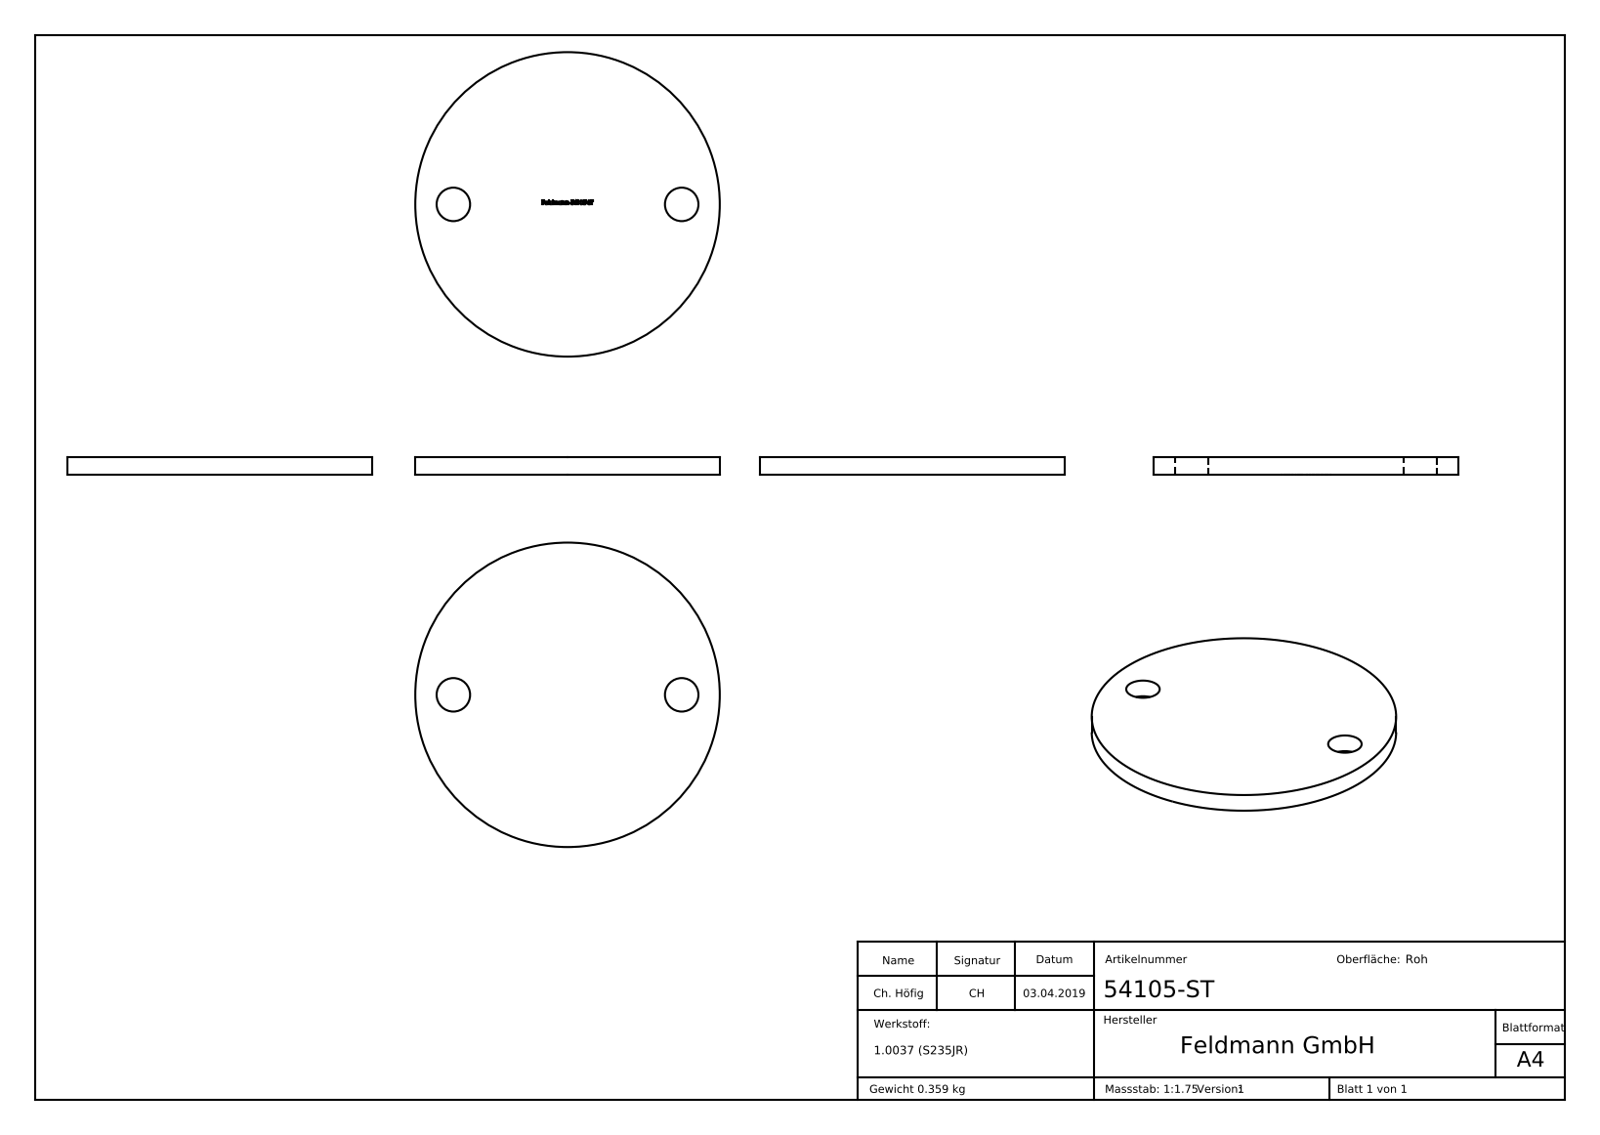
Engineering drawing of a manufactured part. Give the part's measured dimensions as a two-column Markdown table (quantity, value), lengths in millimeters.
| quantity | value |
| --- | --- |
| part name | 54105-ST |
| STEP written by | SolidWorks 2015 (CONFIG_CONTROL_DESIGN) |
| units | millimeters |
| bodies | 1 solid, 216 faces (122 planar, 6 cylindrical, 88 other) |
| overall size | 100 × 100 × 6 |
| volume | 45 983 mm³ |
| surface area | 17 636 mm² |
| round holes (diameter × count) | 11 × 2 |
| round bosses / shafts (diameter × count) | 100 × 1 |
| main face-to-face distances | 6, 5.9, 5.11, 4.31, 0.39, 3.99, 9.72, 2.02, 11.74, 1.32 |
| hole center spacings | 75 |
